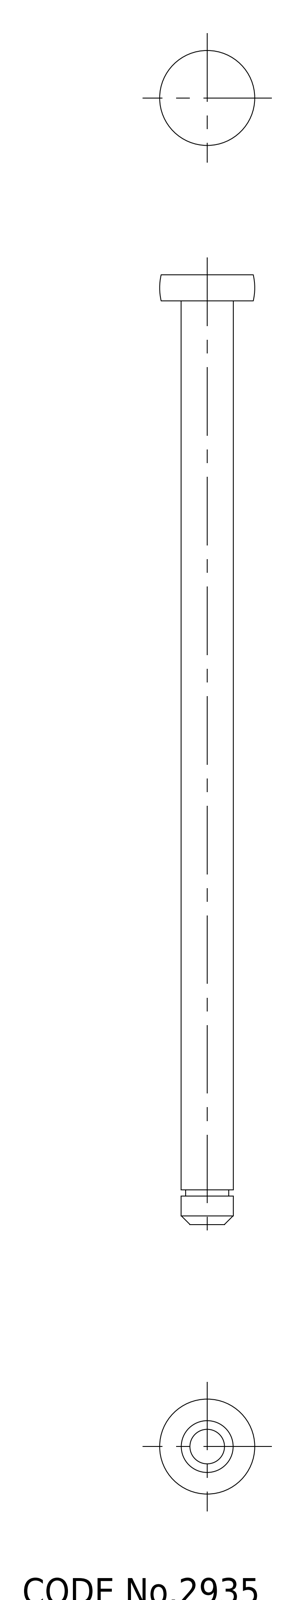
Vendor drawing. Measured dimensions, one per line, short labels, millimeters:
name: TH_121_6_107; shaft
written by: SolidWorks 2015 (AUTOMOTIVE_DESIGN)
unit: mm
bodies: 1 solid, 15 faces (5 planar, 6 cylindrical, 4 other)
size: 110 × 11 × 11
volume: 3 290 mm³; area: 2 302 mm²
bosses: 1× ⌀6, 1× ⌀5
face distances: 3, 107, 110, 4, 103, 106, 3.3, 0.7, 103.7, 106.7
